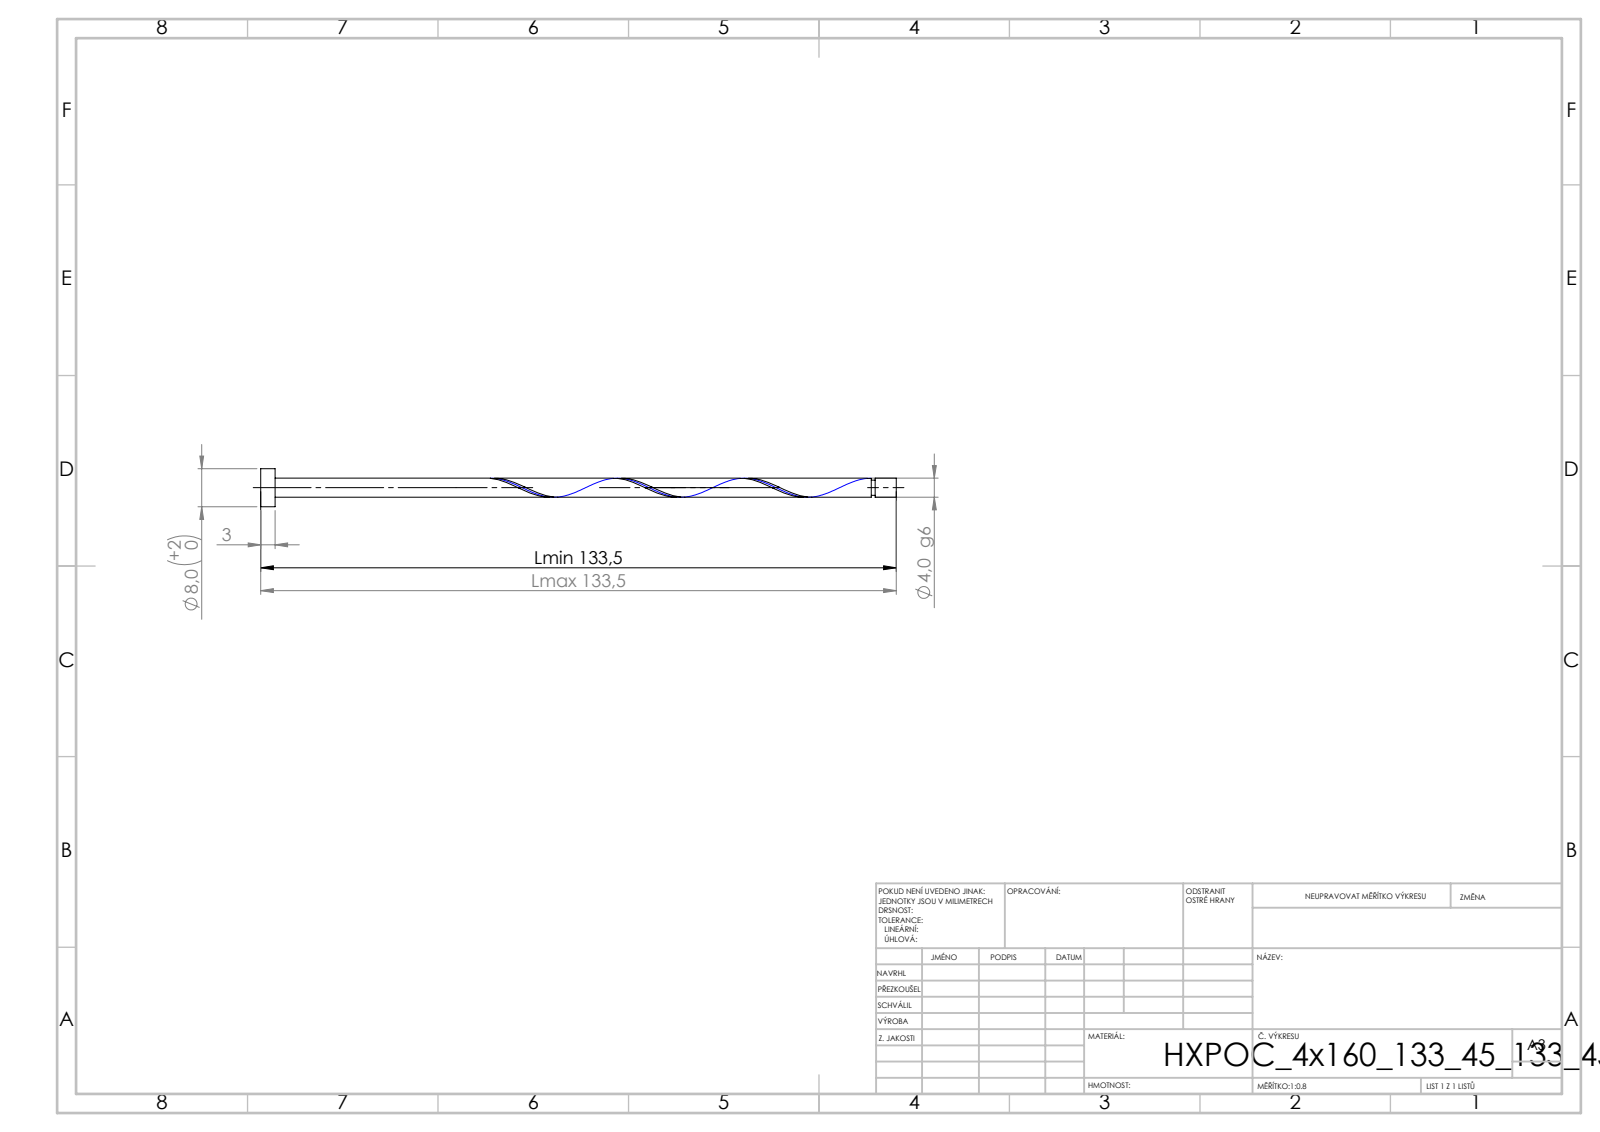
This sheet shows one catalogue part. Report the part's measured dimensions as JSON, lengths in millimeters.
{"step_written_by": "SolidWorks 2019 (CONFIG_CONTROL_DESIGN)", "units": "millimeters", "bodies": {"solids": 1, "faces": 21, "planar": 6, "cylindrical": 14, "other": 1}, "overall_size": [133.45, 8, 8], "volume_mm3": 1767, "surface_area_mm2": 1857, "round_bosses_or_shafts": [[8, 1], [4, 1], [3.2, 1]], "face_to_face_distances": [3, 133.45, 130.45, 129.01, 126.01, 4.44, 128.21, 125.21, 0.8, 5.24]}
